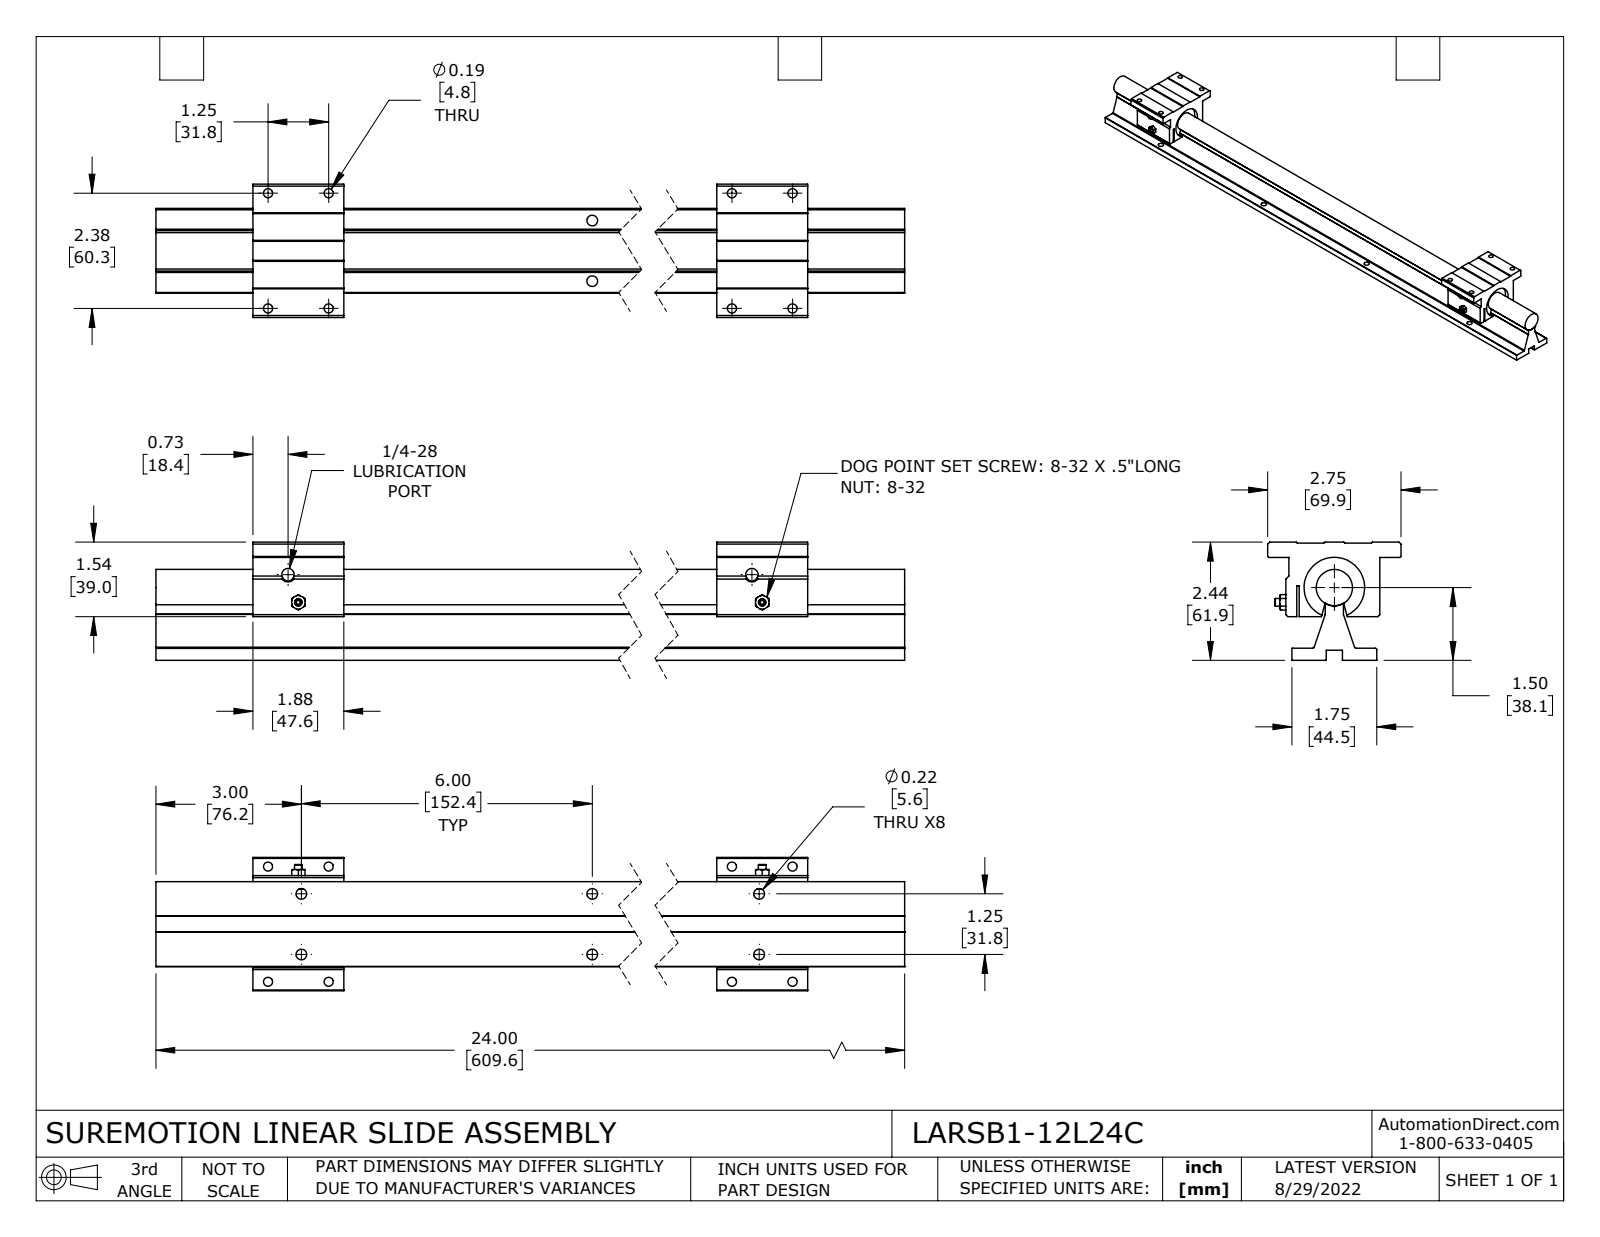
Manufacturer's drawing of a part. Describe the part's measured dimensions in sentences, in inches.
The part is named "LARSACC-005; LARSB1-12L24C-RAIL; LARSB1-12L24C". Its 3-D file was written by "SolidWorks 2021 (CONFIG_CONTROL_DESIGN)". It is 4 solids with 219 faces: 125 planar, 74 cylindrical and 20 other. Overall it measures 24 by 2.75 by 2.437 inches. Its volume is 40.6 cubic inches and its surface area 257.3 square inches. Round holes: 8 of diameter 0.188, 8 of diameter 0.221, 2 of diameter 0.258, 1 of diameter 0.75, 1 of diameter 1.25. Round bosses or shafts: 2 of diameter 0.157. Partial cylindrical surfaces (rounded edges, fillets, slot ends): 11 of radius 0.03, 1 of radius 0.06, 1 of radius 0.374. The main face-to-face distances are 0.25, 0.71, 1.04, 0.687, 1.062, 0.022, 0.352, 0.21, 0.04, 0.062. The hole center spacings are 1.25, 6, 6.129, 18.125, 2.376, 2.684, 5.467, 5.731.
